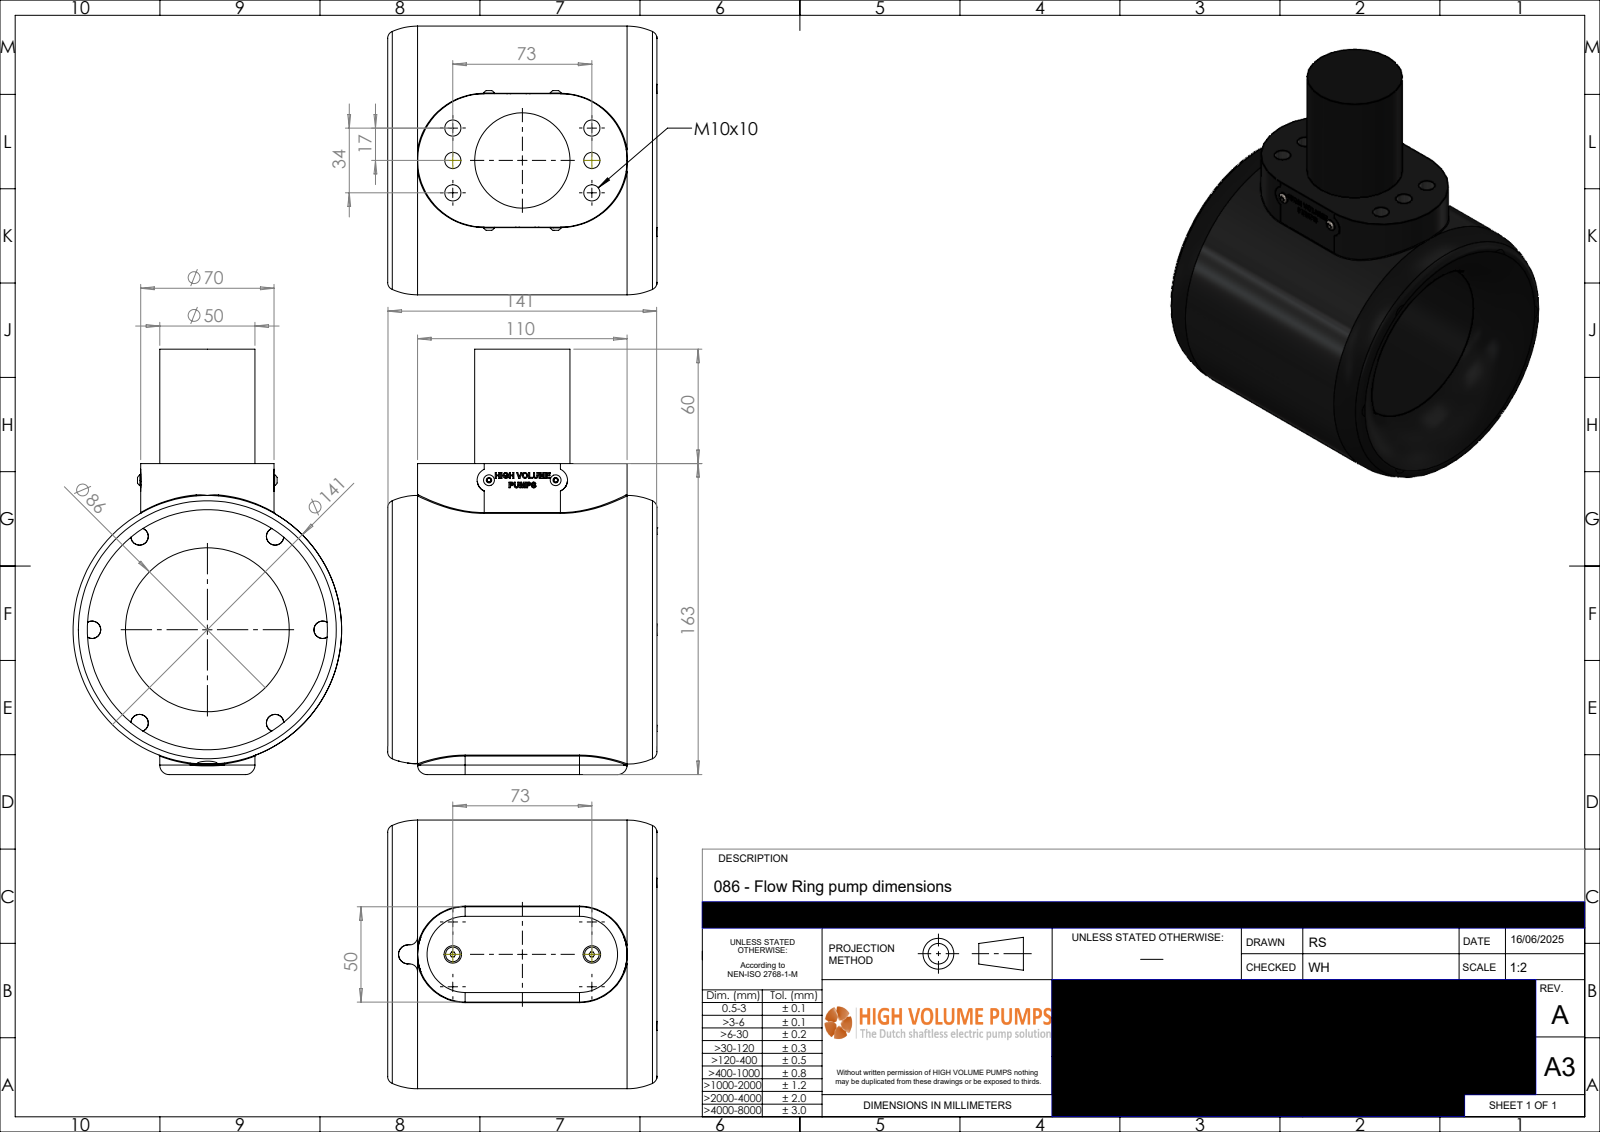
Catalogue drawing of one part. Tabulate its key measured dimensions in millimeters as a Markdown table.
| quantity | value |
| --- | --- |
| part name | P-086-030-rev-A-FR |
| STEP written by | SolidWorks 2024 (AUTOMOTIVE_DESIGN) |
| units | millimeters |
| bodies | 1 solid, 580 faces (354 planar, 49 cylindrical, 177 other) |
| overall size | 223.22 × 141.35 × 141 |
| volume | 1 558 000 mm³ |
| surface area | 130 969 mm² |
| round holes (diameter × count) | 8.5 × 6, 86.01 × 1 |
| round bosses / shafts (diameter × count) | 7.64 × 2, 5.7 × 2, 141 × 1, 50 × 1 |
| partial cylindrical surfaces (radius × count) | 0.5 × 4, 5 × 3, 4 × 2, 6.15 × 2, 6.25 × 2, 25 × 2, 34.5 × 2, 35 × 2 |
| main face-to-face distances | 163.22, 60, 223.22, 70, 10, 153.78, 9.44, 69.44, 50, 69.9 |
| hole center spacings | 17, 74.95, 73, 34, 80.53 |
